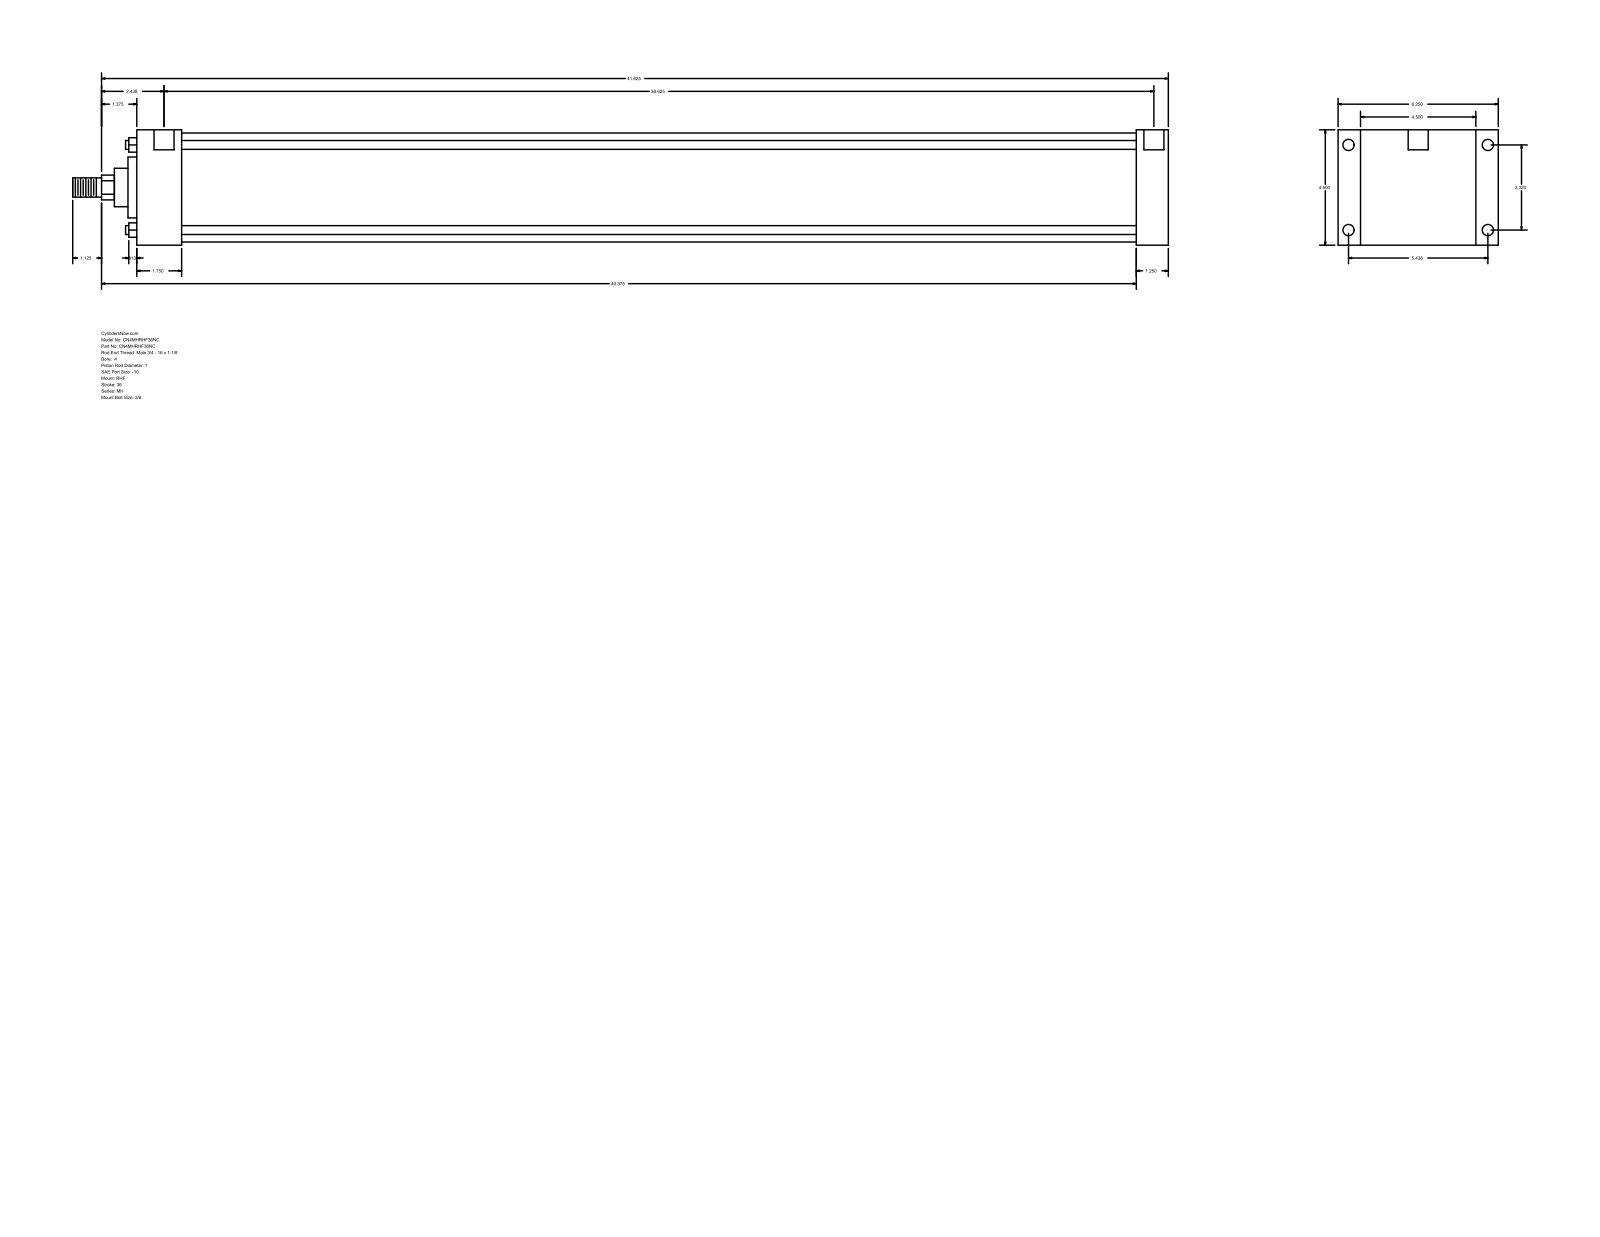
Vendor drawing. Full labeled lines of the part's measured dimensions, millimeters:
Part name (STEP PRODUCT): MH_RHF__0400_1
STEP written by: GSSL Pune (CONFIG_CONTROL_DESIGN)
Units: millimetres
Bodies: 0 solids, 90 faces (61 planar, 29 cylindrical, 0 other)
Overall size (bounding box): 1085.85 × 158.75 × 114.3
Round holes (diameter × count): ⌀8.73 ×4, ⌀11.13 ×4, ⌀19.84 ×2
Round bosses / shafts (diameter × count): ⌀8.76 ×4, ⌀107.95 ×1, ⌀60.33 ×1, ⌀38.1 ×1, ⌀25.4 ×1, ⌀19.05 ×1
Partial cylindrical surfaces — rounded edges, fillets, slot ends (radius × count): R12.29 ×1
Main face-to-face distances: 114.3, 1022.36, 990.61, 31.75, 22.23, 136.53, 44.46, 946.15, 977.9, 158.76
Hole centre spacings: 84.32, 138.12, 161.82, 984.25, 1.58, 1.59, 981.08, 982.66
